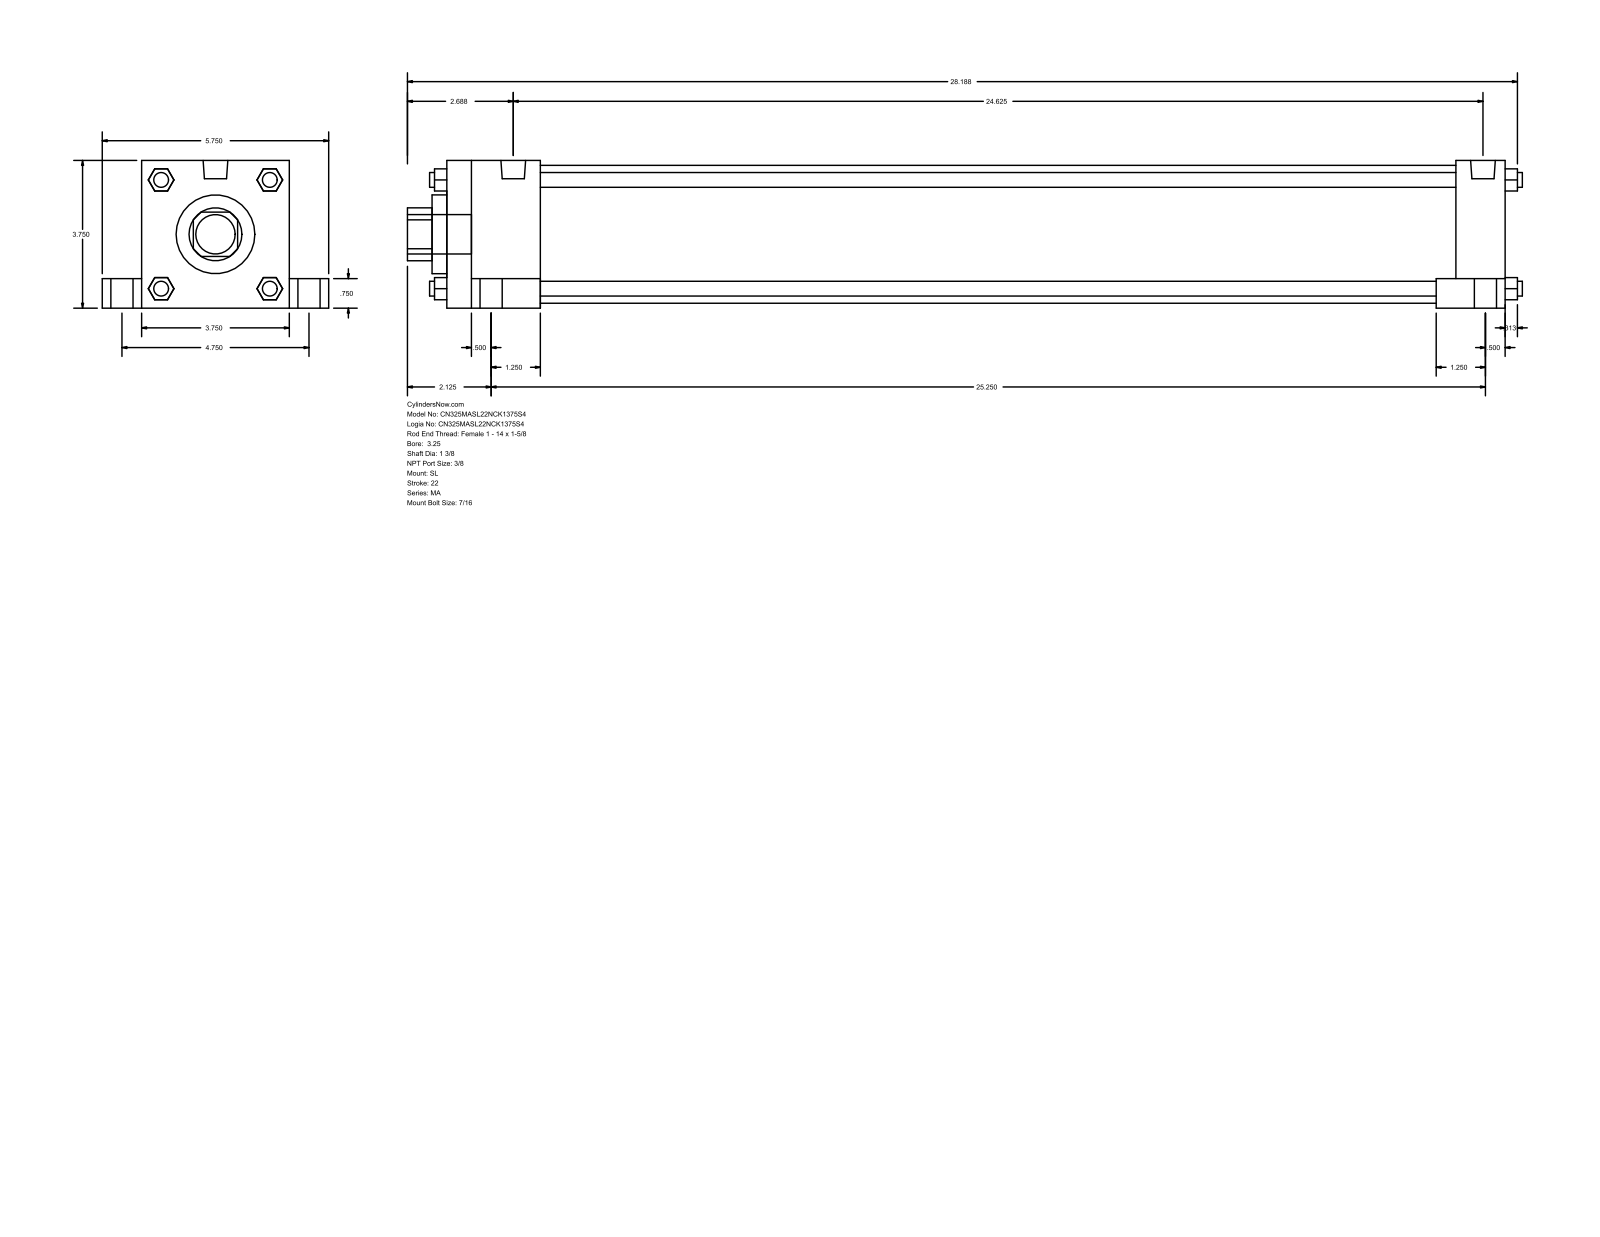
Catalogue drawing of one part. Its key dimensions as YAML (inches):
part_name: "MA_SL__0325_1.375"
step_written_by: "GSSL Pune (CONFIG_CONTROL_DESIGN)"
units: inches
bodies: {solids: 0, faces: 148, planar: 112, cylindrical: 36, other: 0}
overall_size: [28.313, 5.75, 3.75]
round_holes:
  - {diameter: 1.375, count: 1}
  - {diameter: 2, count: 1}
  - {diameter: 3.5, count: 1}
round_bosses_or_shafts:
  - {diameter: 0.813, count: 4}
  - {diameter: 0.563, count: 4}
  - {diameter: 0.437, count: 4}
  - {diameter: 0.375, count: 4}
  - {diameter: 0.627, count: 2}
  - {diameter: 1, count: 1}
partial_cylinders:
  - {radius: 0.672, count: 1}
face_to_face_distances: [3.75, 26.875, 23.25, 1, 4.75, 25.625, 1.25, 2.375, 24.5, 0.75]
